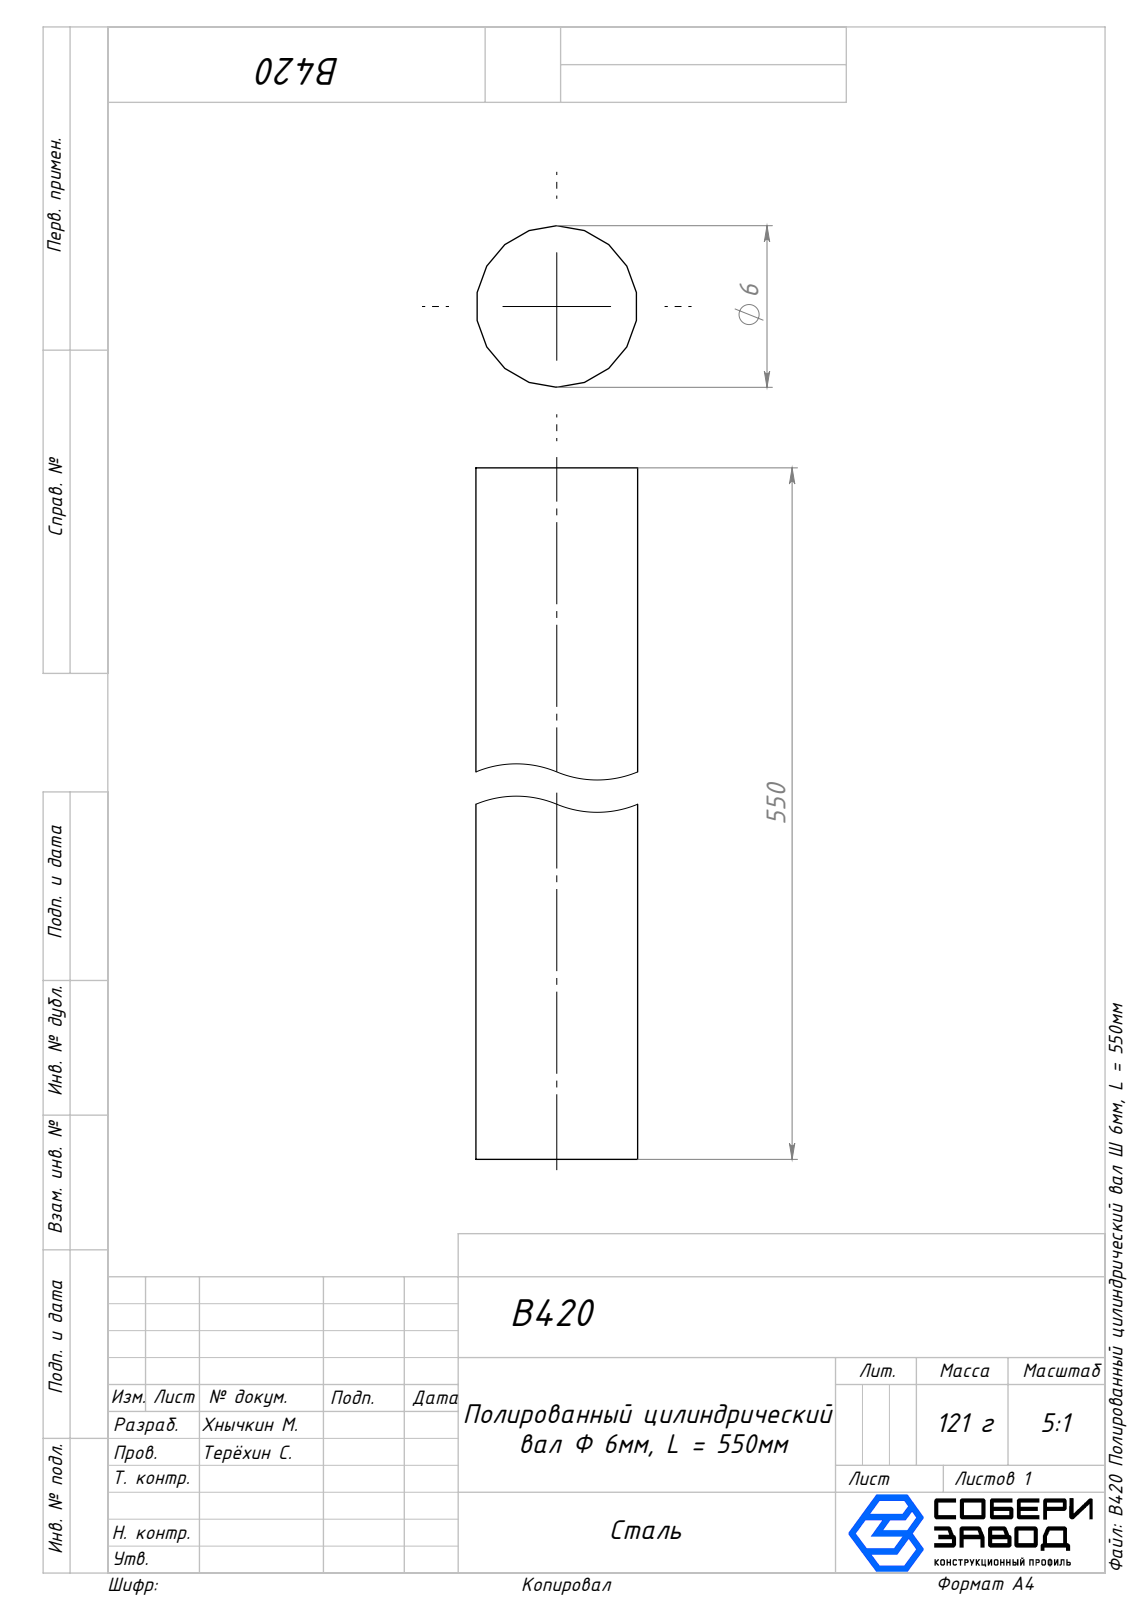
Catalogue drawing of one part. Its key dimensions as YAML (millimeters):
part_name: "B420 Полированный цилиндрический вал Ø 6мм, L = 550мм"
step_written_by: "SolidWorks 2025 (AUTOMOTIVE_DESIGN)"
units: millimeters
bodies: {solids: 1, faces: 4, planar: 2, cylindrical: 2, other: 0}
overall_size: [550, 6, 6]
volume: 15551
surface_area: 10424
round_bosses_or_shafts:
  - {diameter: 6, count: 1}
face_to_face_distances: [550]
